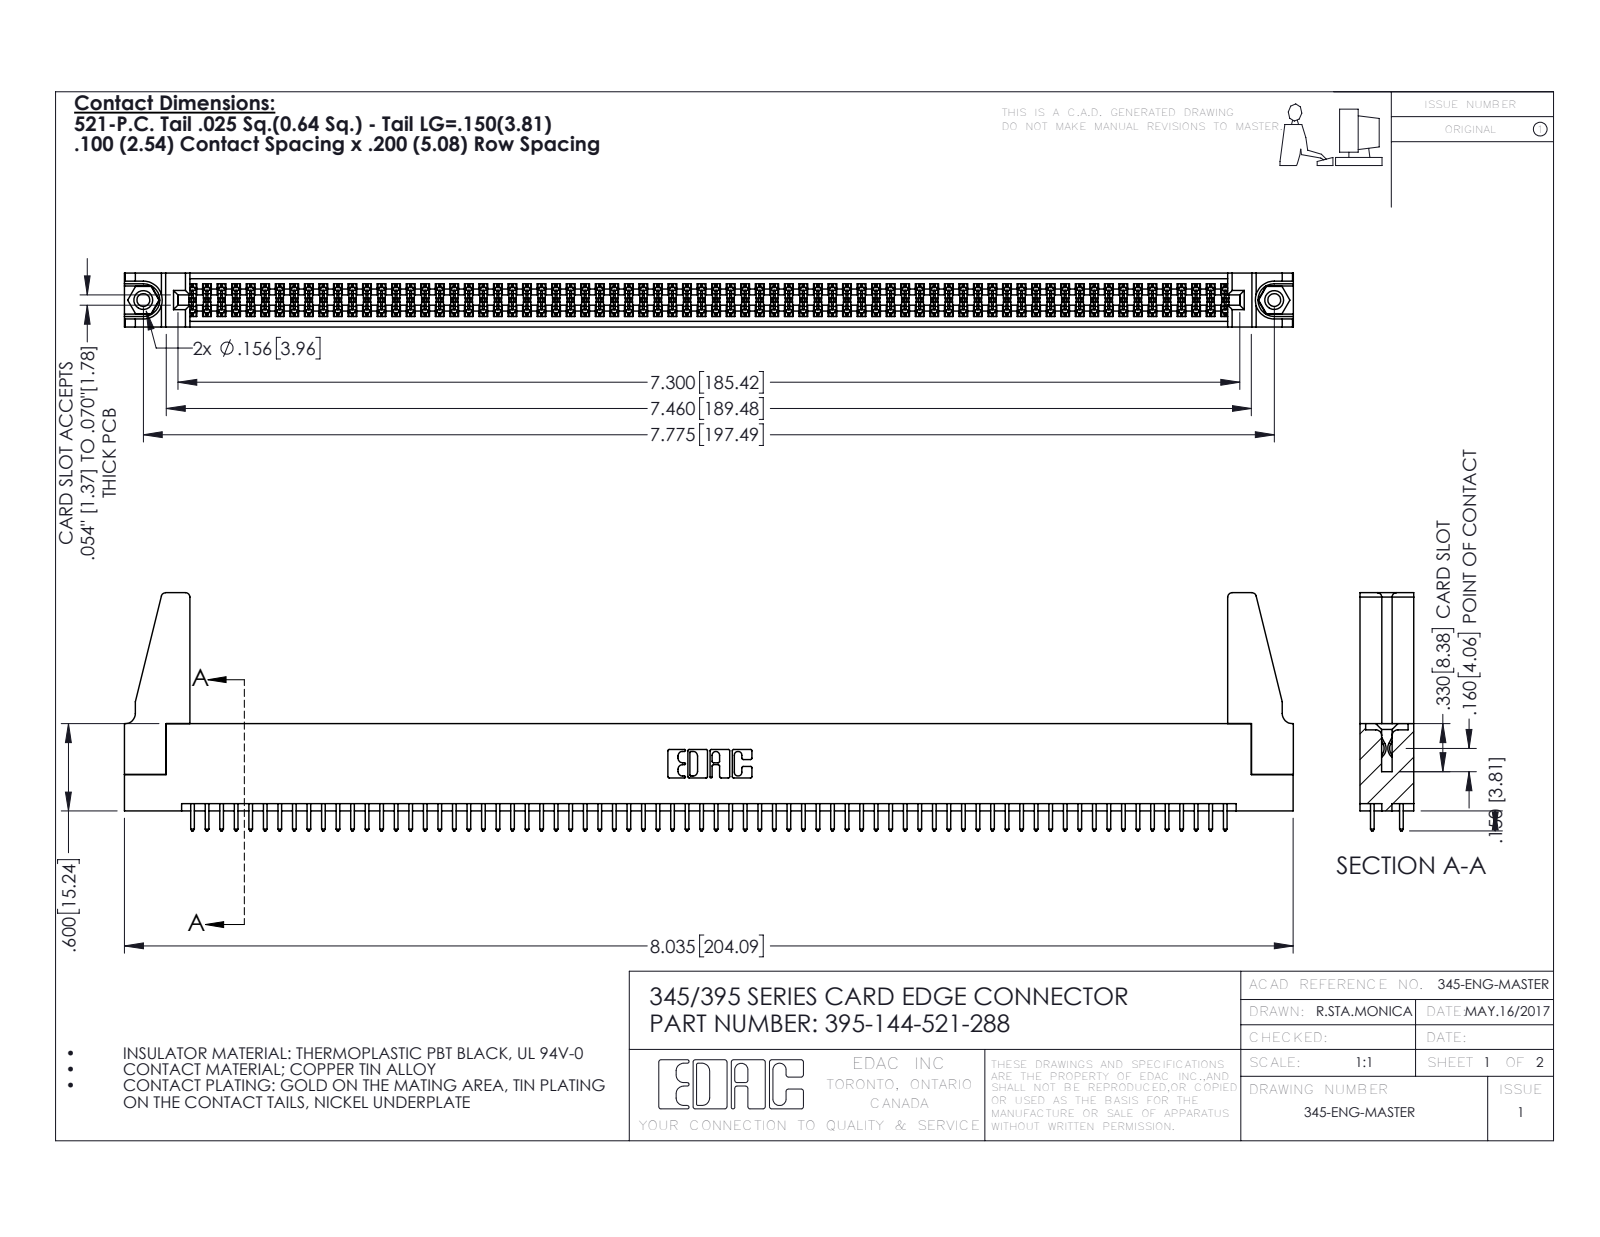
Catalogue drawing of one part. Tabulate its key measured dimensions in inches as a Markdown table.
| quantity | value |
| --- | --- |
| part name | 395-144-521-288; 345-250-001_345-250-001-102; 345-220-078_345-220-088; 345-292-001_345-293-121 (+1 more) |
| STEP written by | SolidWorks 2016 (CONFIG_CONTROL_DESIGN) |
| units | inches |
| bodies | 149 solids, 7450 faces (4904 planar, 2530 cylindrical, 16 other) |
| overall size | 8.036 × 1.637 × 0.37 |
| volume | 1.422 in³ |
| surface area | 51.08 in² |
| round holes (diameter × count) | 0.089 × 2, 0.125 × 2, 0.156 × 2, 0.064 × 1 |
| round bosses / shafts (diameter × count) | 0.155 × 2 |
| partial cylindrical surfaces (radius × count) | 0.006 × 216, 0.01 × 144, 0.01 × 22, 0.03 × 8, 0.007 × 6, 0.031 × 6, 0.026 × 3, 0.014 × 2 |
| main face-to-face distances | 0.072, 0.298, 0.37, 0.2, 0.098, 0.272, 0.025, 0.225, 0.175, 0.149 |
| hole center spacings | 0.27, 7.539, 7.775 |
